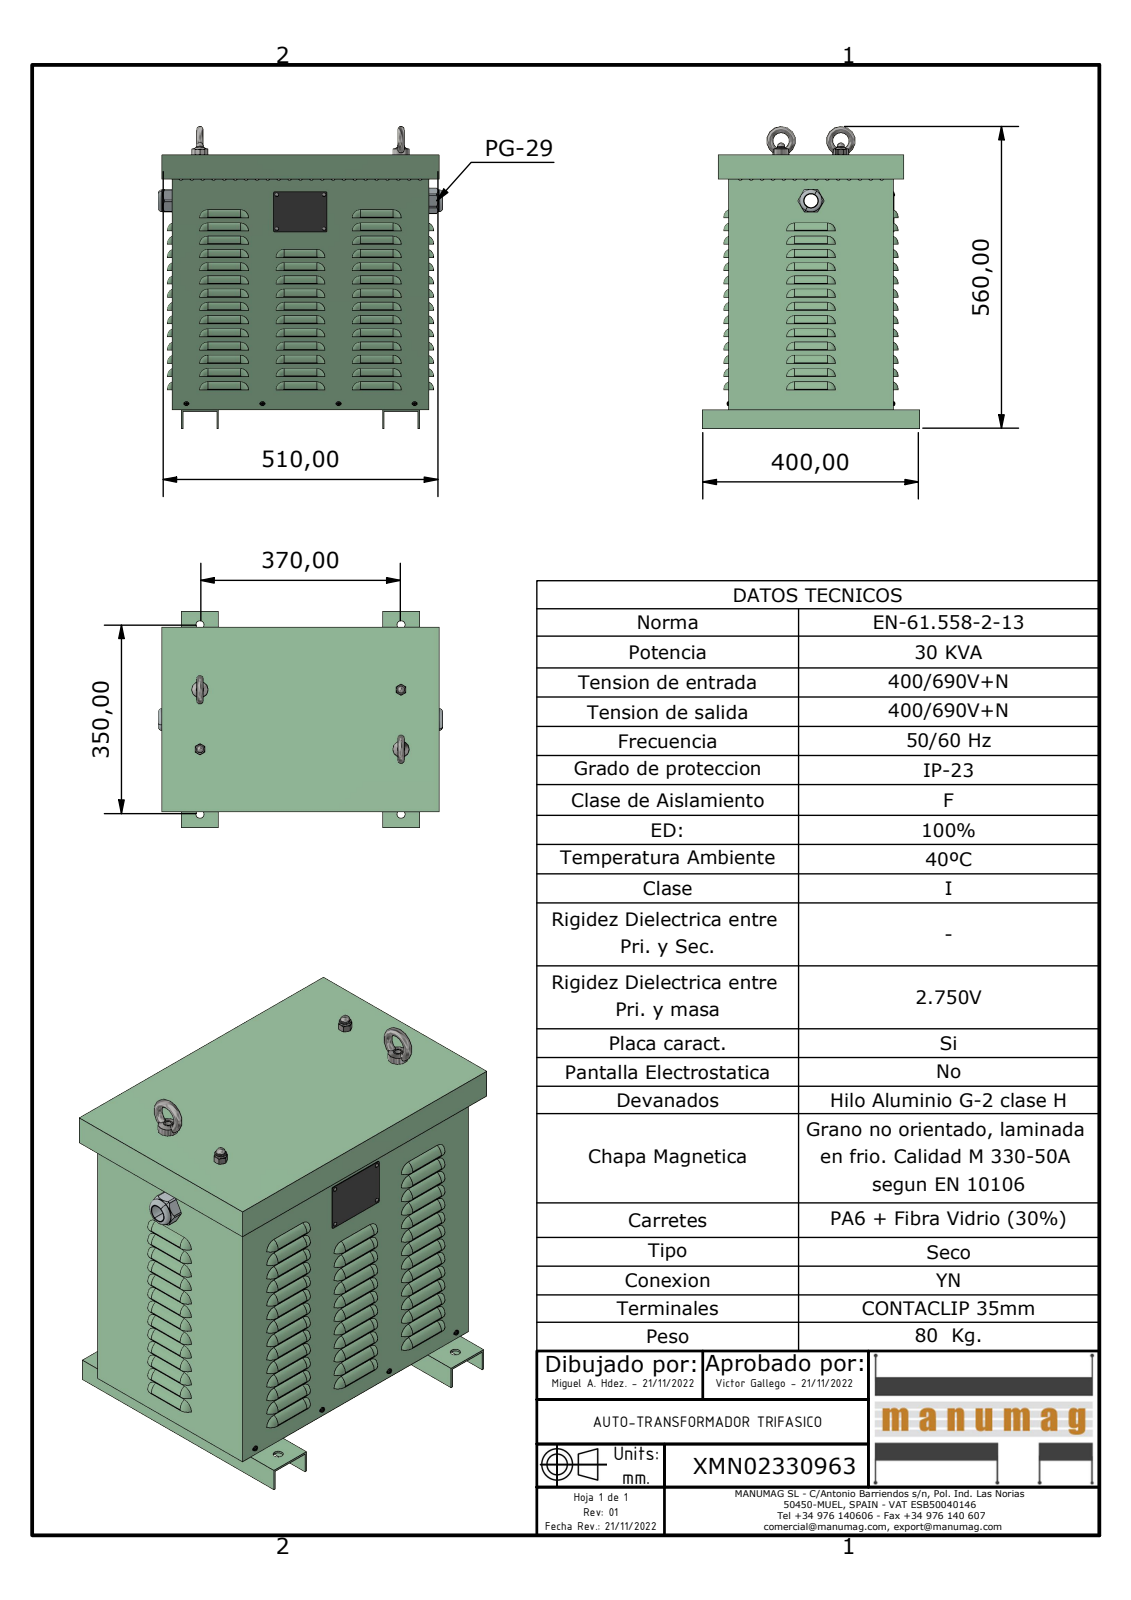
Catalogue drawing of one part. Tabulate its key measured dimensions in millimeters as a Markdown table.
| quantity | value |
| --- | --- |
| part name | XMN02330963; JE030 CUERPO; JE030 BASE; JE030 PATAS (+7 more) |
| STEP written by | Autodesk Inventor 2023 (AUTOMOTIVE_DESIGN) |
| units | millimeters |
| bodies | 24 solids, 2363 faces (789 planar, 948 cylindrical, 626 other) |
| overall size | 560 × 523.4 × 400 |
| volume | 2 982 000 mm³ |
| surface area | 2 640 000 mm² |
| round holes (diameter × count) | 11 × 260, 15 × 8, 4 × 4, 5 × 4, 10.11 × 4, 14 × 4, 25 × 1, 38 × 1 |
| round bosses / shafts (diameter × count) | 4 × 4, 3.62 × 4, 3.2 × 4, 30 × 2, 18 × 2, 13.6 × 2, 40.8 × 1, 37.3 × 1 |
| partial cylindrical surfaces (radius × count) | 14 × 104, 5 × 74, 7 × 54, 15 × 54, 3.22 × 12, 2.5 × 8, 2 × 4, 23.85 × 1 |
| main face-to-face distances | 2, 470, 301, 472, 468, 299, 303, 19, 3, 21 |
| hole center spacings | 31.76, 71.59, 15, 28, 70, 44.6, 99.14, 140.8 |
